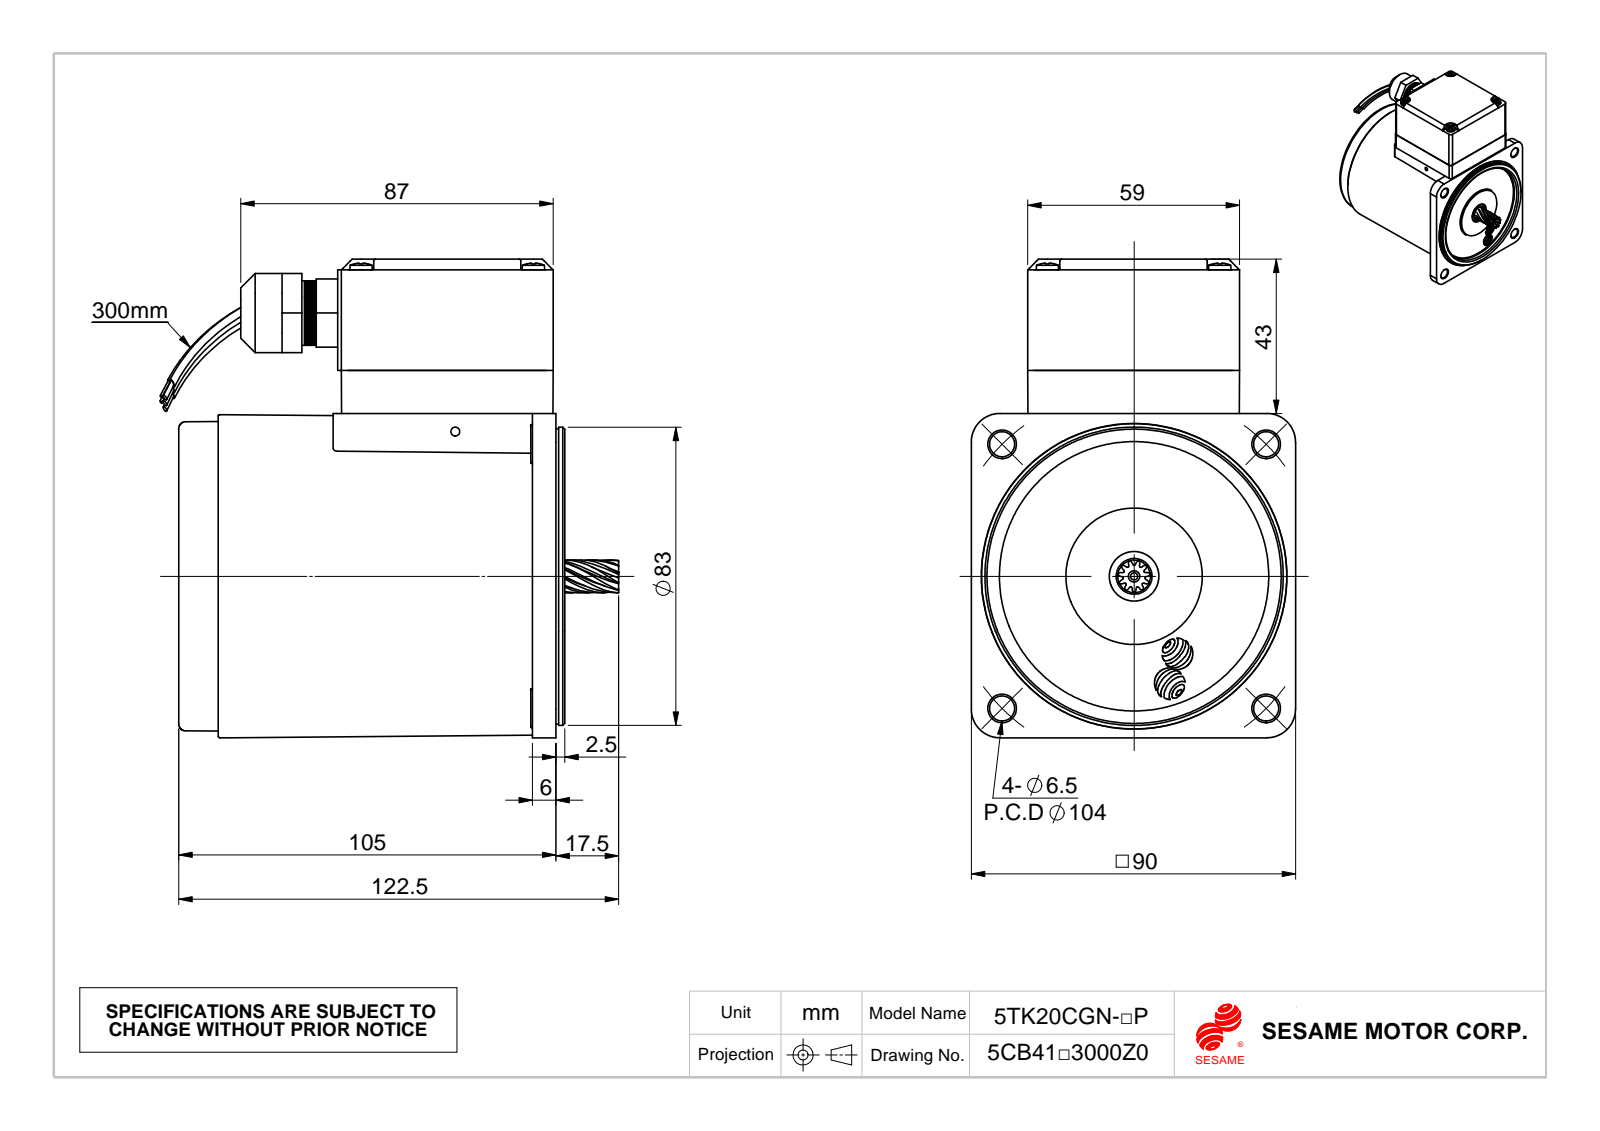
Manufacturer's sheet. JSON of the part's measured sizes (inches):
{"part_name": "M540Ts; 成品180度; Ts下墊片; 40GN", "step_written_by": "SolidWorks 2010 (CONFIG_CONTROL_DESIGN)", "units": "inches", "bodies": {"solids": 14, "faces": 2619, "planar": 224, "cylindrical": 944, "other": 1451}, "overall_size": [5.248, 5.028, 3.555], "volume_in3": 20.75, "surface_area_in2": 199.7, "round_holes": [[0.13, 4], [0.138, 4], [0.154, 4], [0.169, 4], [0.276, 4], [0.079, 1], [0.098, 1], [0.433, 1], [0.472, 1], [0.539, 1], [0.571, 1], [0.827, 1]], "round_bosses_or_shafts": [[0.248, 4], [0.118, 4], [0.394, 2], [3.316, 1], [3.268, 1], [3.236, 1], [1.496, 1], [1.378, 1]], "partial_cylinders_radius": [[0.079, 12], [0.02, 8], [0.031, 8], [0.059, 8], [0.065, 8], [0.115, 8], [0.157, 8], [0.008, 4]], "face_to_face_distances": [0.472, 0.039, 3.606, 4.075, 0.059, 3.898, 0.291, 0.03, 0.138, 1.693], "hole_center_spacings": [1.89, 2.047, 2.895, 0.459, 0.486, 0.5, 0.981, 0.984]}
